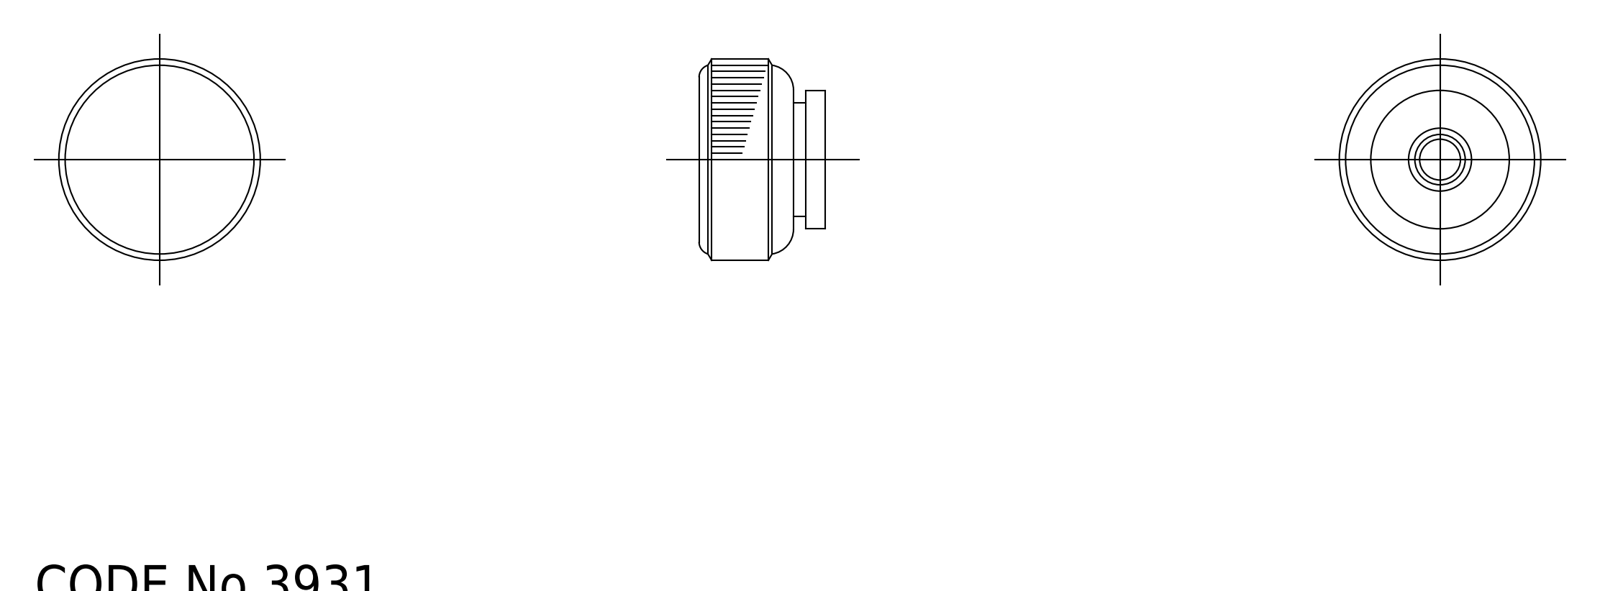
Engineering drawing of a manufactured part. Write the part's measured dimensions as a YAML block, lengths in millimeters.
part_name: "knob"
step_written_by: "CADfix (AUTOMOTIVE_DESIGN)"
units: millimeters
bodies: {solids: 1, faces: 23, planar: 0, cylindrical: 0, other: 23}
overall_size: [16, 16, 10]
volume: 1528
surface_area: 905
